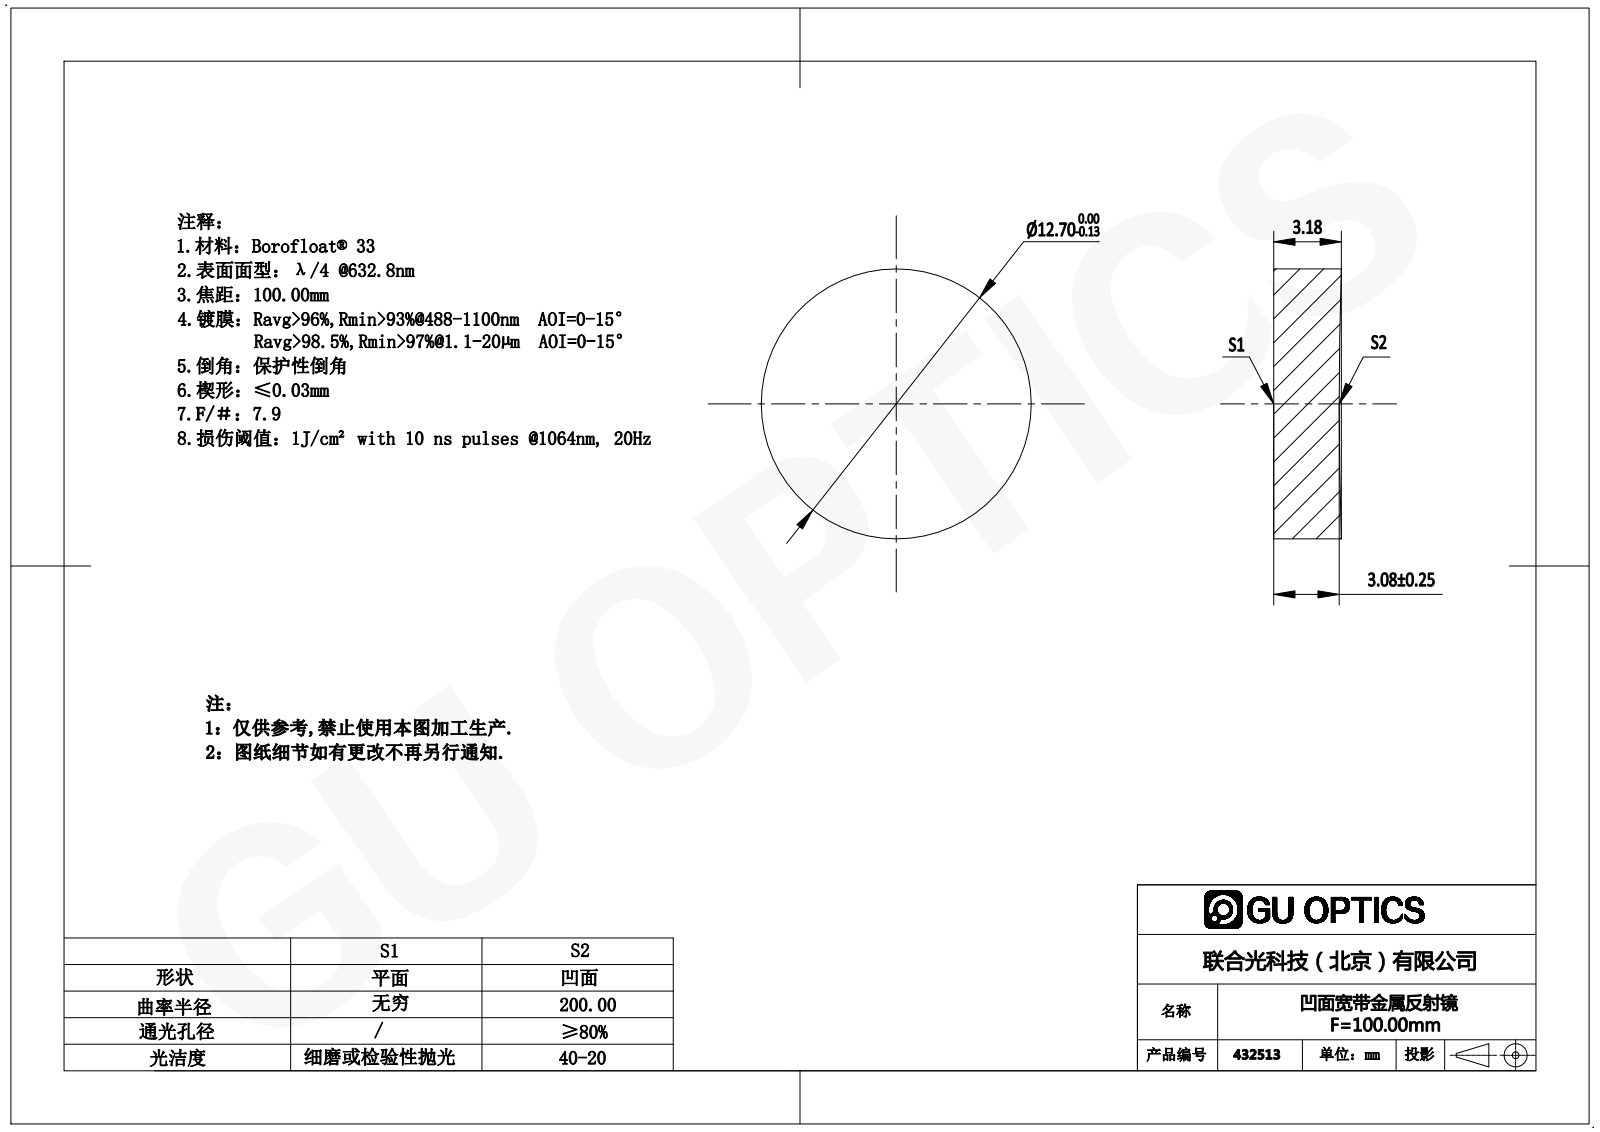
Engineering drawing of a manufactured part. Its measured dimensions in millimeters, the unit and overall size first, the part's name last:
Units: millimetres
Overall size (bounding box): 12.7 × 12.7 × 3.18
Round bosses / shafts (diameter × count): ⌀12.7 ×1
Volume: 397 mm³ · Surface area: 380 mm²
Bodies: 1 solid, 5 faces (1 planar, 2 cylindrical, 2 other)
Part name (STEP PRODUCT): 432503
STEP written by: SolidWorks 2016 (AUTOMOTIVE_DESIGN)
